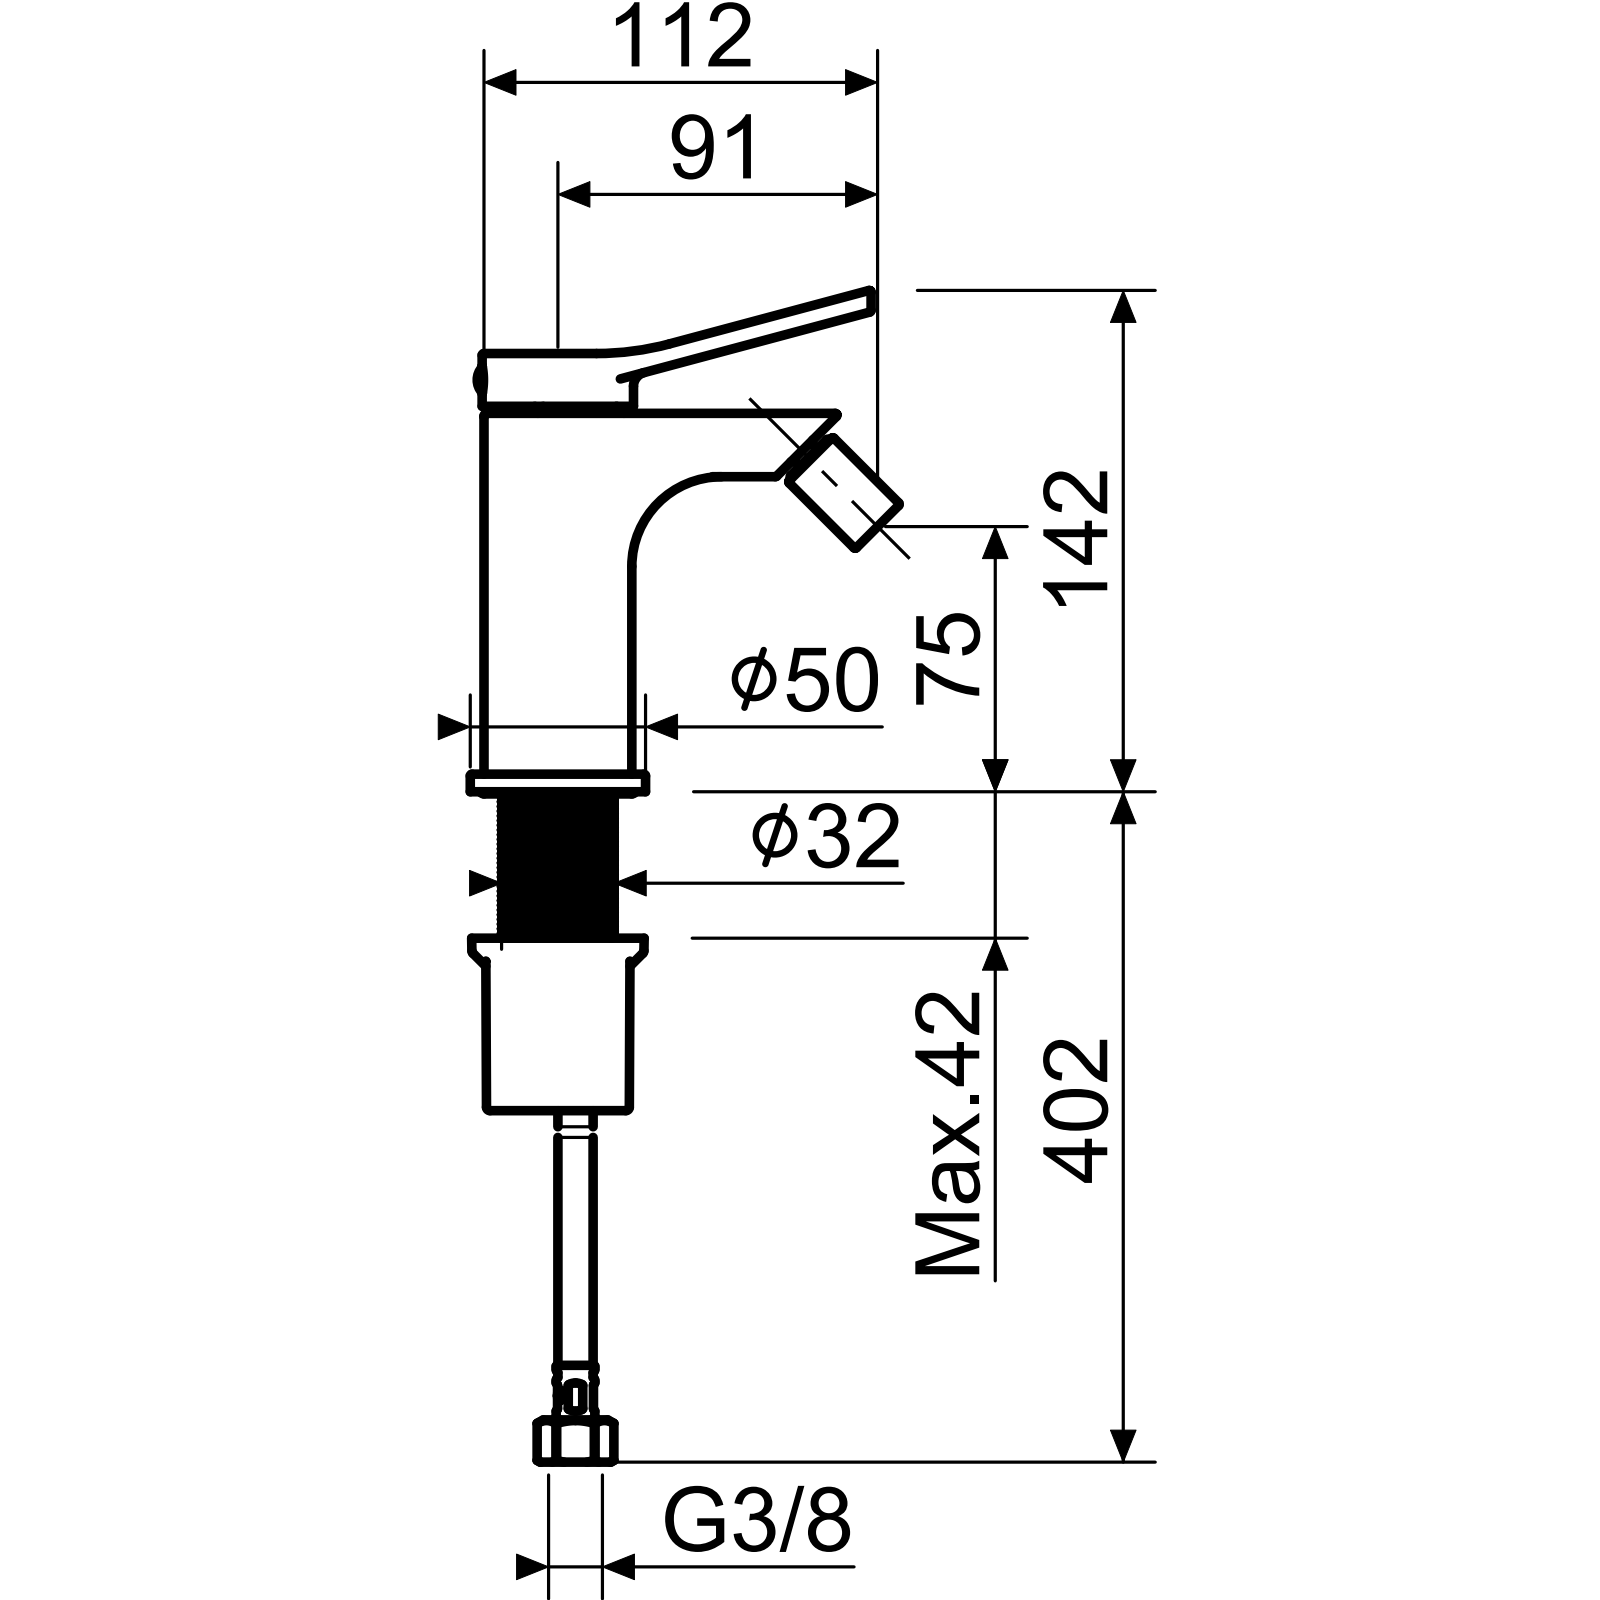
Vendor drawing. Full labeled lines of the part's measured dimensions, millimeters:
Part name (STEP PRODUCT): AKBR301C001; SCCMAC0006; AKBR005C001; SBTMAC0001 (+4 more)
STEP written by: CREO PARAMETRIC BY PTC INC, 2020281 (CONFIG_CONTROL_DESIGN)
Units: millimetres
Bodies: 7 solids, 2366 faces (1176 planar, 602 cylindrical, 588 other)
Overall size (bounding box): 172.59 × 161.7 × 49.8
Volume: 84 208 mm³ · Surface area: 63 979 mm²
Round holes (diameter × count): ⌀13 ×2, ⌀3 ×1, ⌀5 ×1, ⌀6 ×1, ⌀6.6 ×1, ⌀8 ×1, ⌀11 ×1, ⌀13.01 ×1, ⌀14.2 ×1, ⌀15 ×1, ⌀16 ×1, ⌀16.5 ×1
Round bosses / shafts (diameter × count): ⌀12 ×2, ⌀49.8 ×1, ⌀43 ×1, ⌀42 ×1, ⌀40 ×1, ⌀38 ×1, ⌀37.65 ×1, ⌀36.7 ×1
Partial cylindrical surfaces — rounded edges, fillets, slot ends (radius × count): R0.12 ×19, R0.1 ×16, R0.5 ×15, R1 ×8, R96.73 ×8, R107.49 ×8, R119.67 ×8, R138.88 ×8
Main face-to-face distances: 2, 5.99, 2.8, 14.5, 16.5, 17.3, 19.3, 122, 99.7, 102.5
Hole centre spacings: 1, 9.75
